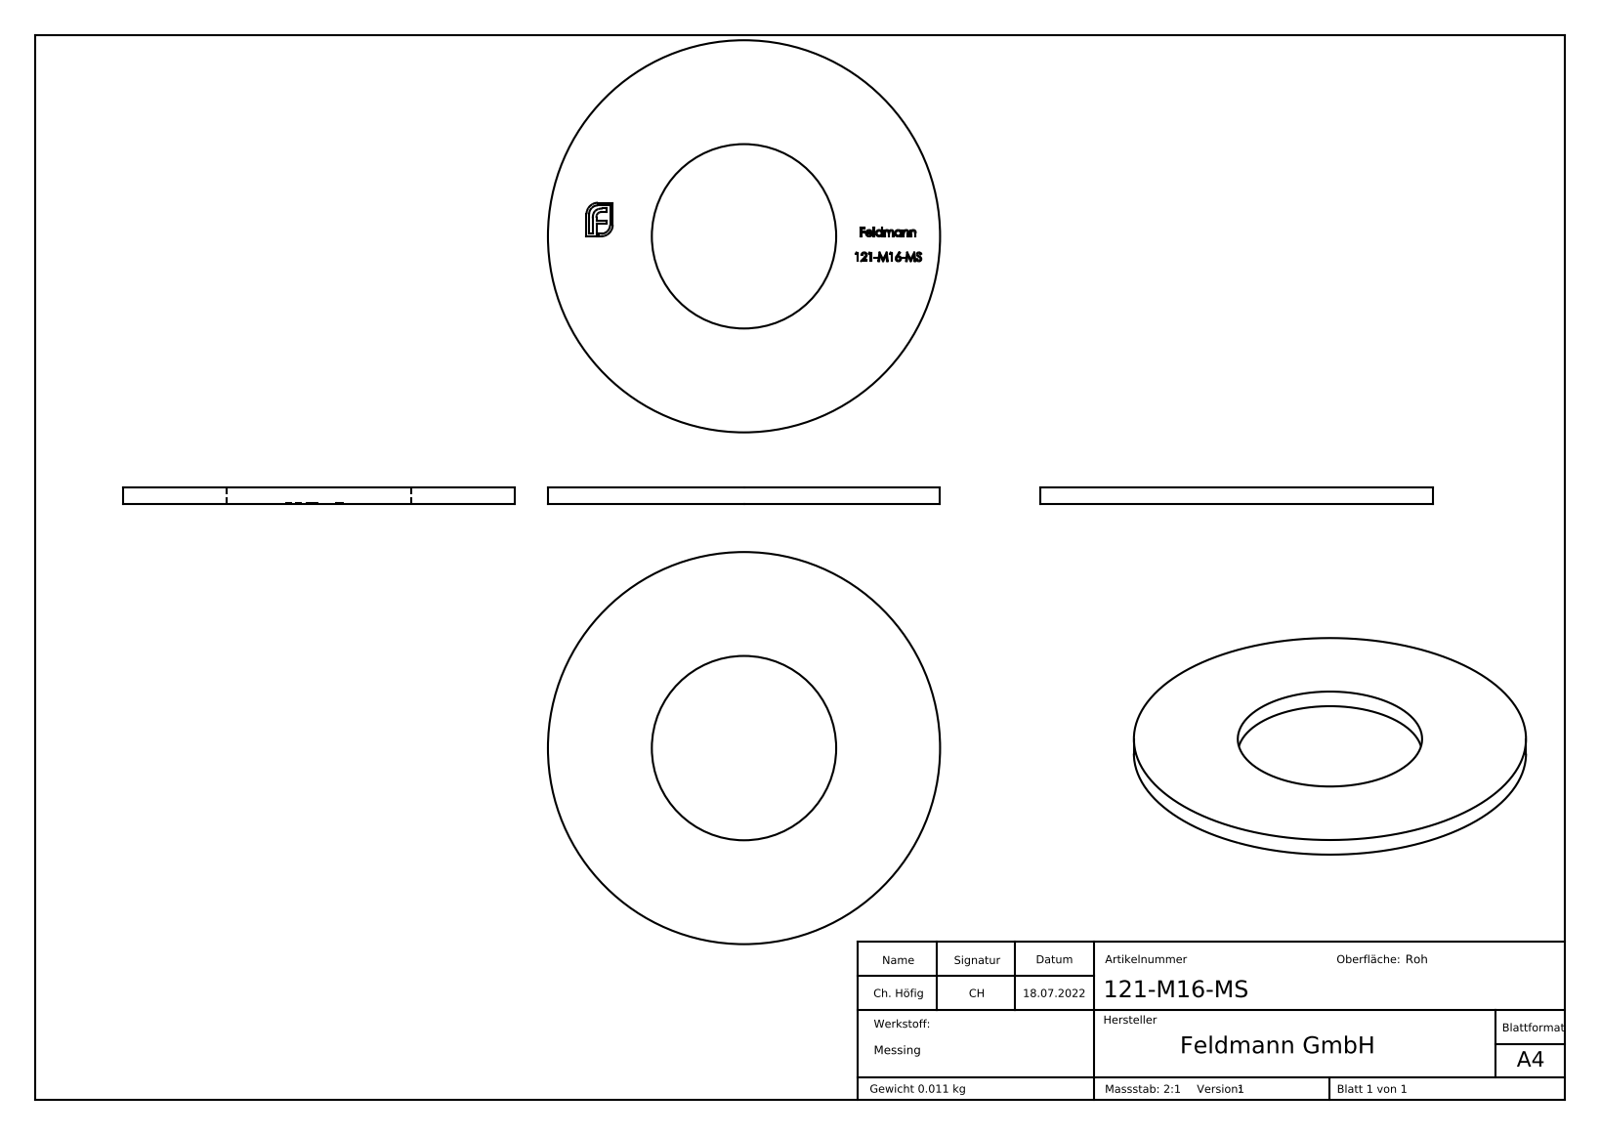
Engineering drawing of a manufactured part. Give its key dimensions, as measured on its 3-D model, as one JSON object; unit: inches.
{"part_name": "121-M16-MS", "step_written_by": "SolidWorks 2018 (CONFIG_CONTROL_DESIGN)", "units": "inches", "bodies": {"solids": 1, "faces": 264, "planar": 164, "cylindrical": 2, "other": 98}, "overall_size": [1.449, 1.449, 0.063], "volume_in3": 0.081, "surface_area_in2": 3.002, "round_holes": [[0.681, 1]], "round_bosses_or_shafts": [[1.449, 1]], "face_to_face_distances": [0.063, 0.059, 0.013, 0.091, 0.087, 0.013, 0.101, 0.077, 0.064, 0.977]}
